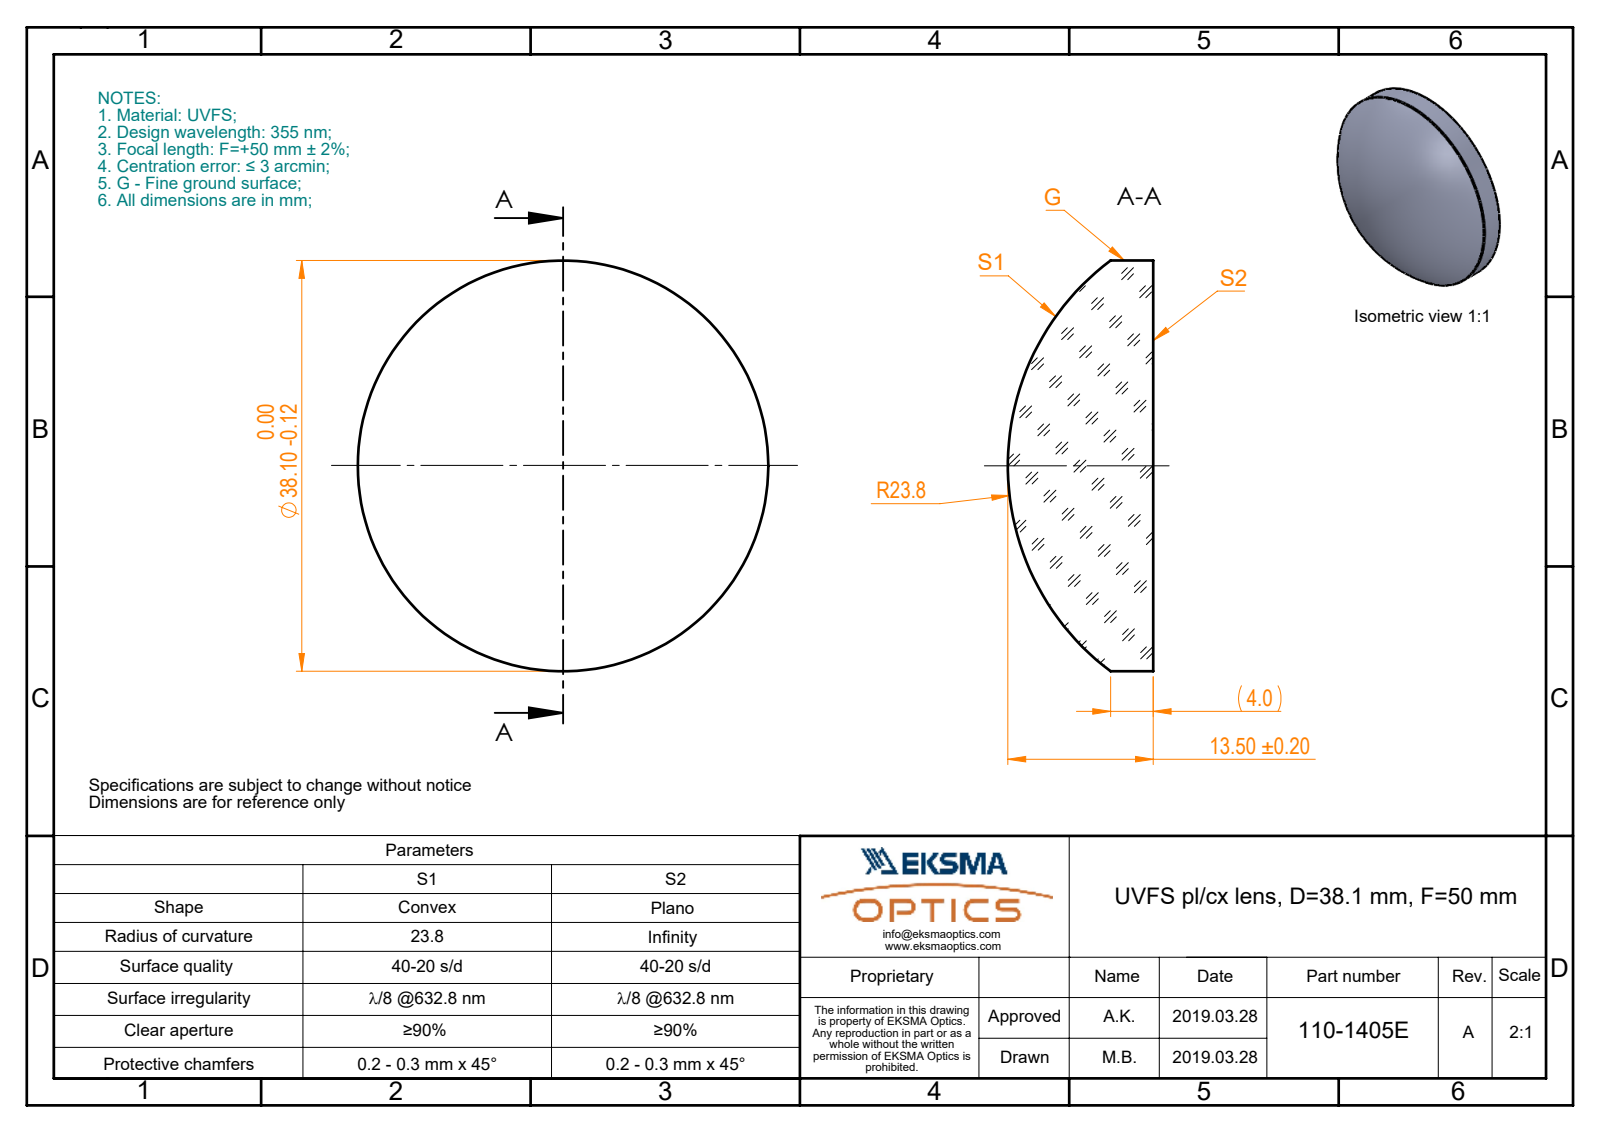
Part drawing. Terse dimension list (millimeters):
name: 110-1405E UVFS pl-cx 38.1 F50
written by: SolidWorks 2017 (CONFIG_CONTROL_DESIGN)
unit: mm
bodies: 1 solid, 5 faces (1 planar, 2 cylindrical, 2 other)
size: 38.1 × 38.1 × 13.5
volume: 10 410 mm³; area: 3 040 mm²
bosses: 1× ⌀38.1
